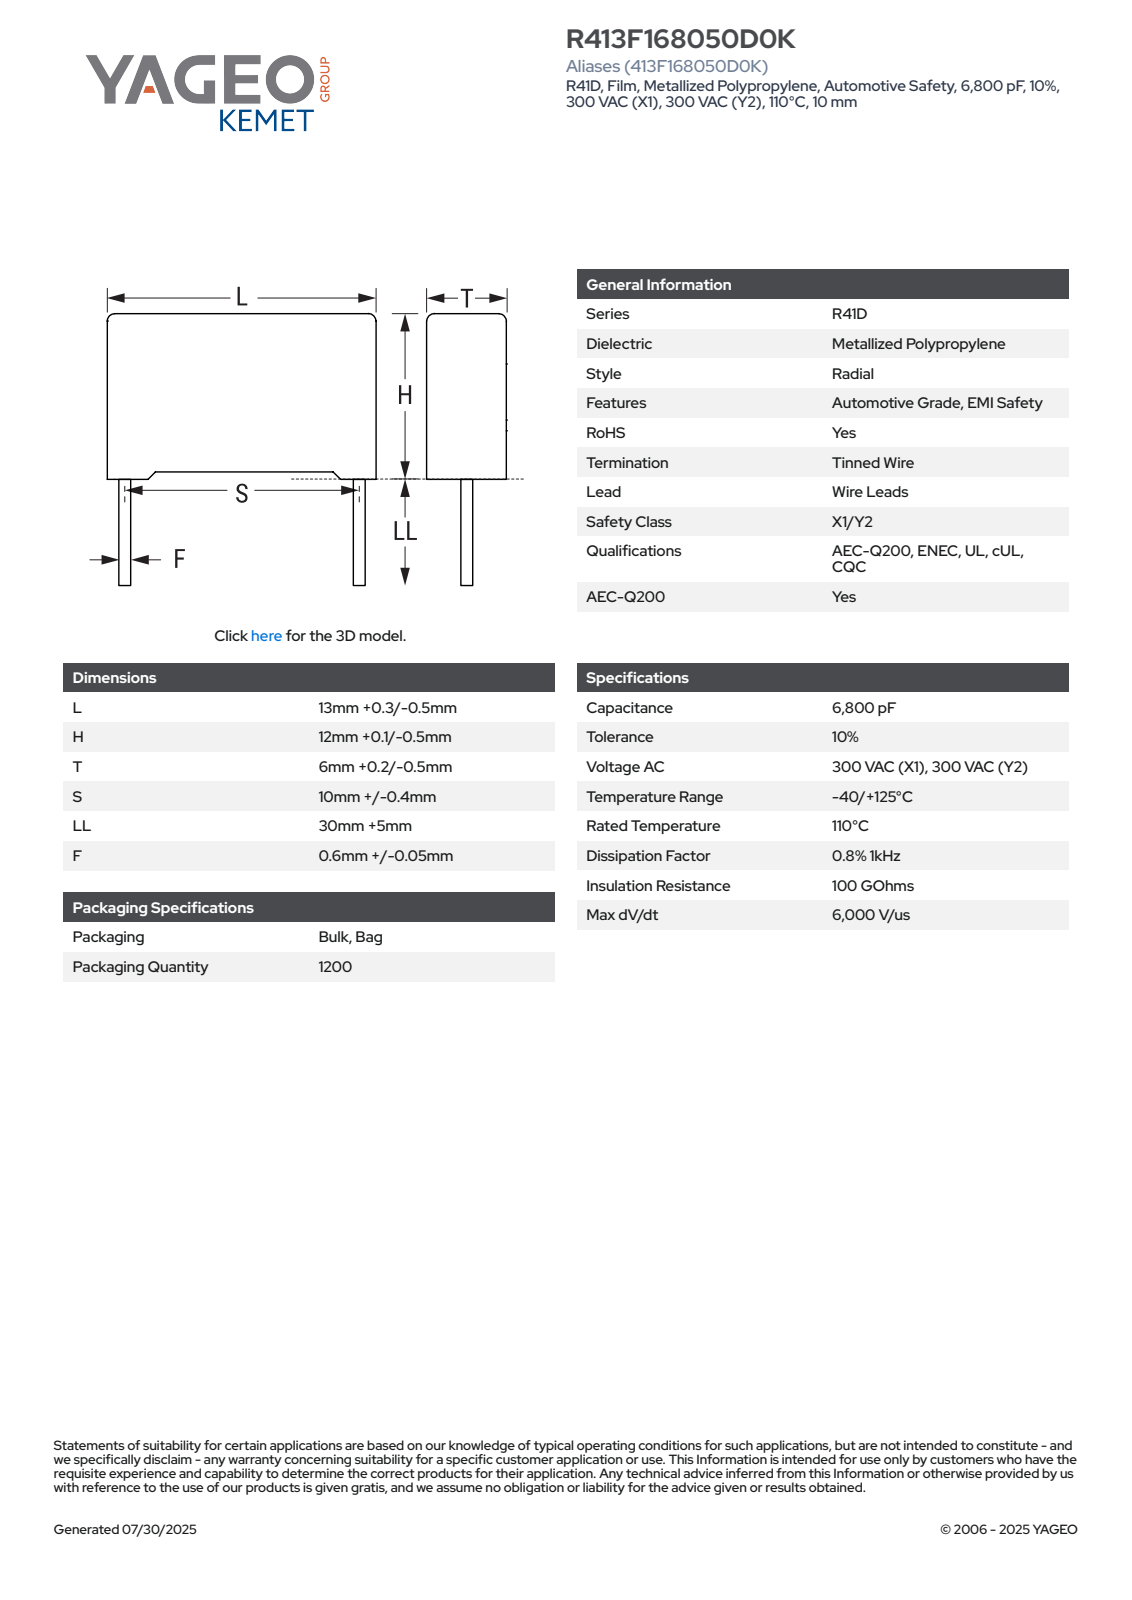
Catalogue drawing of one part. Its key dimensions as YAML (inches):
part_name: "CFR_RB2_13X12X6_L13.3H12.1T6.2S10LL35F0.65"
step_written_by: "SolidWorks 2021 (AUTOMOTIVE_DESIGN)"
units: inches
bodies: {solids: 4, faces: 85, planar: 77, cylindrical: 8, other: 0}
overall_size: [1.854, 0.524, 0.244]
volume: 0.059
surface_area: 1.25
round_bosses_or_shafts:
  - {diameter: 0.026, count: 2}
partial_cylinders:
  - {radius: 0.02, count: 4}
face_to_face_distances: [0.244, 0.524, 0.447, 0.017, 0.227, 0.03, 0.476, 0.506, 0.209, 0.017]
